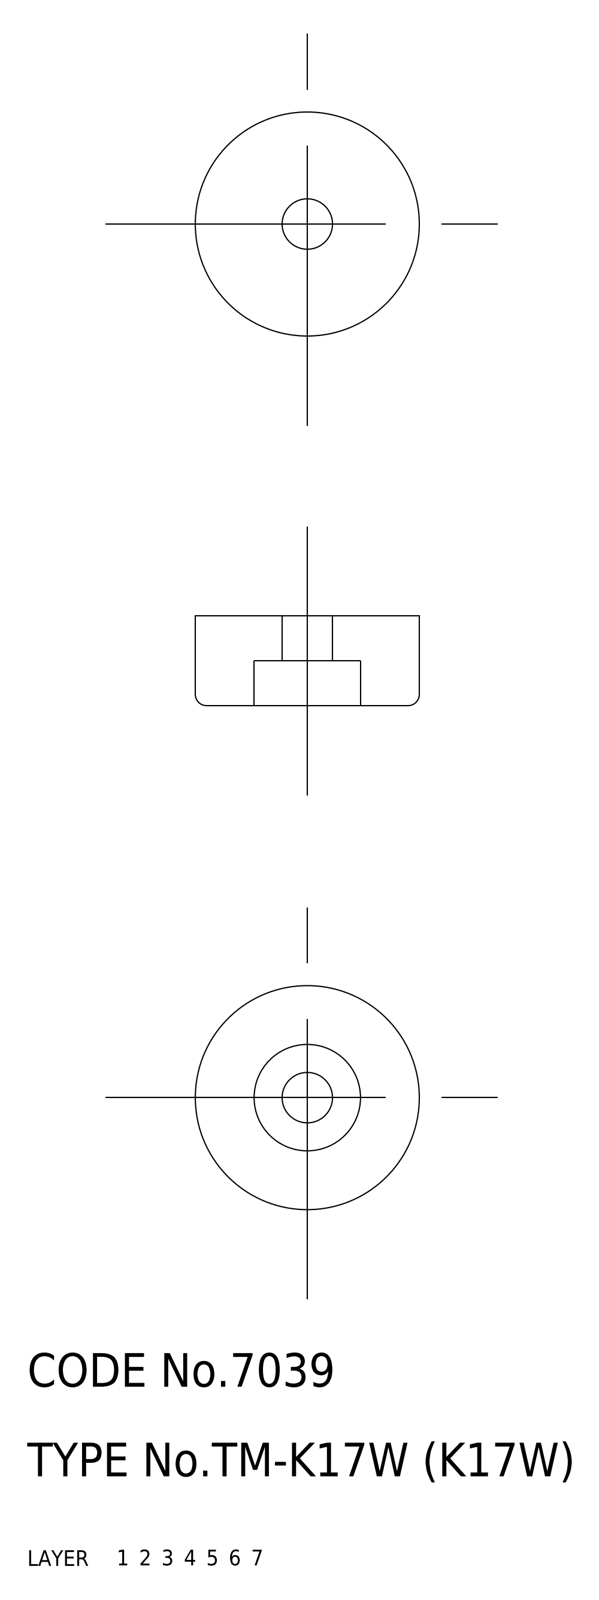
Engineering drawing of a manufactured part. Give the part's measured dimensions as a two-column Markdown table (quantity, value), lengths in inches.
| quantity | value |
| --- | --- |
| part name | washer; rubber foot; K17W_6162_36 |
| STEP written by | CADfix (AUTOMOTIVE_DESIGN) |
| units | inches |
| bodies | 2 solids, 23 faces (0 planar, 0 cylindrical, 23 other) |
| overall size | 0.787 × 0.787 × 0.315 |
| volume | 0.132 in³ |
| surface area | 2.463 in² |
